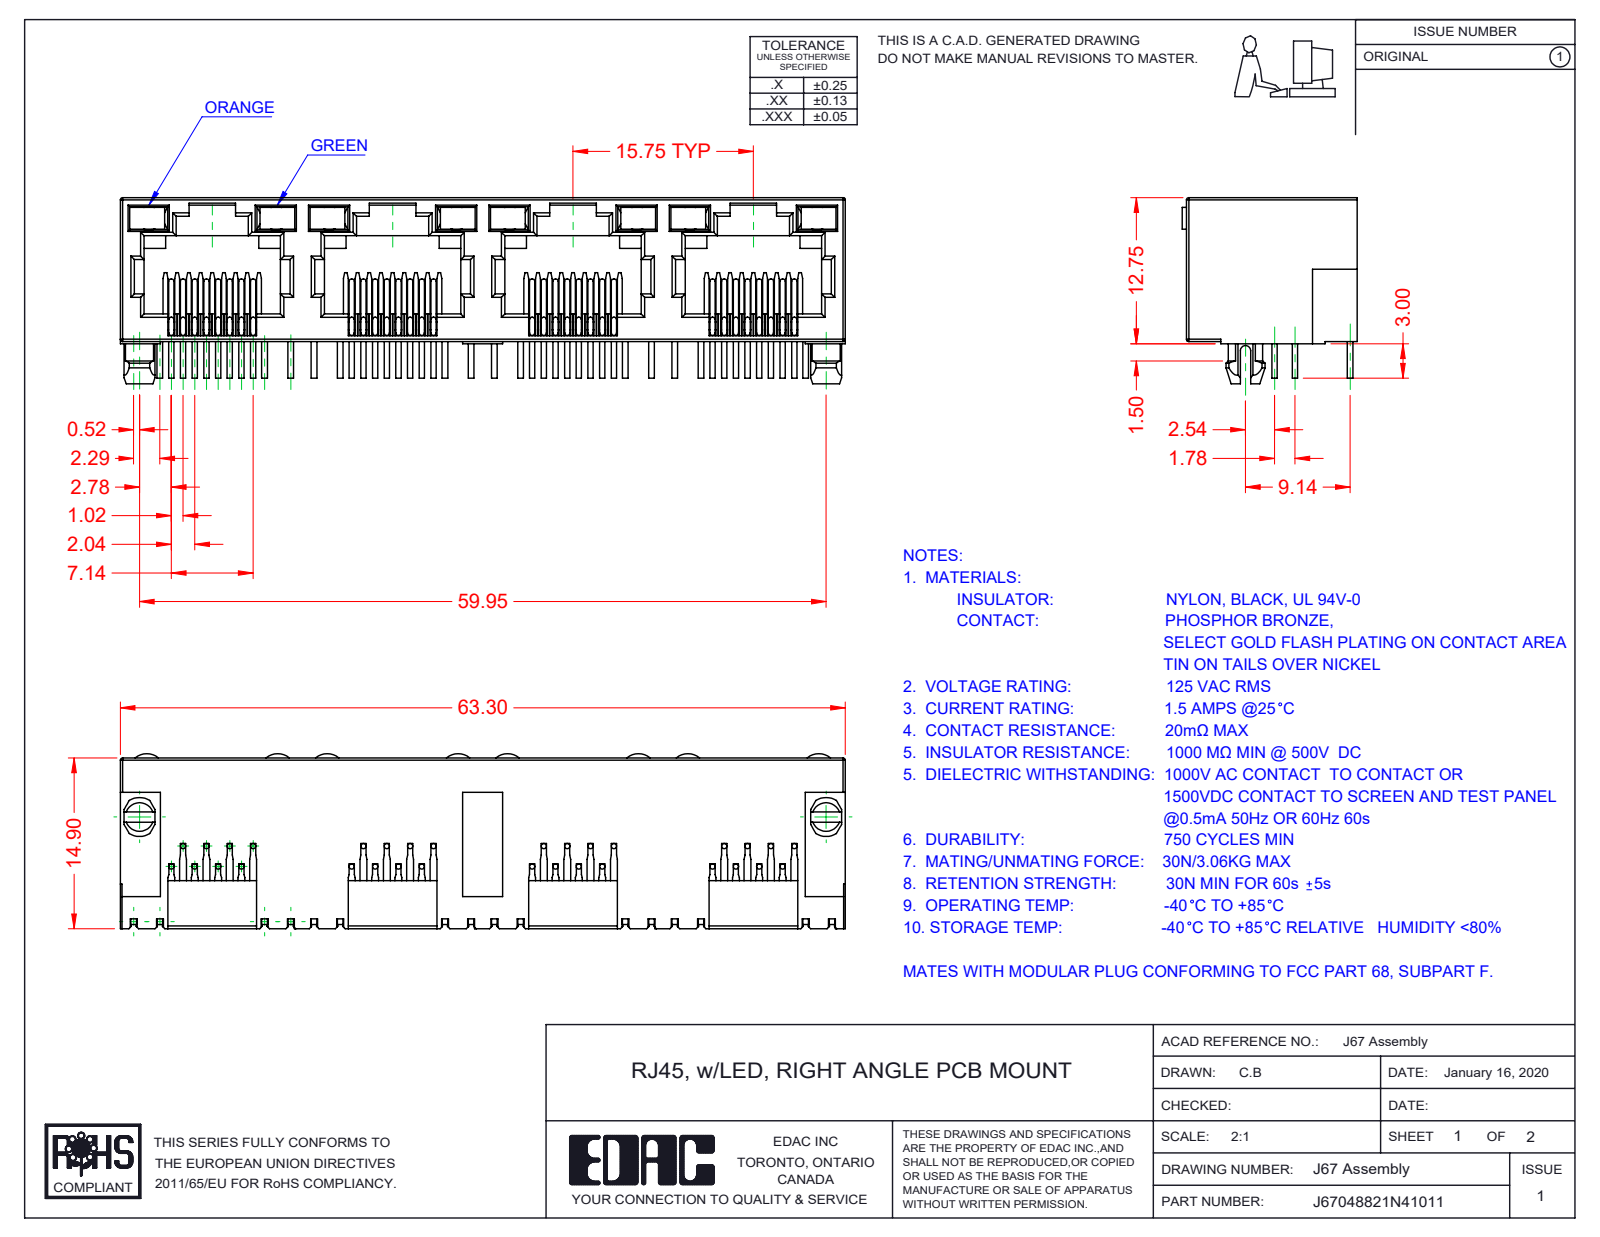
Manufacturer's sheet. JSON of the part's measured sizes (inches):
{"part_name": "67 Insulator; J67048822N43011; 67 LED RH_3-Green; 67 LED LH_4-Orange (+1 more)", "step_written_by": "SolidWorks 2016 (CONFIG_CONTROL_DESIGN)", "units": "inches", "bodies": {"solids": 41, "faces": 2465, "planar": 1781, "cylindrical": 476, "other": 208}, "overall_size": [2.492, 0.64, 0.602], "volume_in3": 0.315, "surface_area_in2": 17.94, "round_bosses_or_shafts": [[0.018, 96]], "partial_cylinders_radius": [[0.008, 66], [0.012, 29], [0.018, 9], [0.061, 8], [0.059, 2], [0.067, 2], [0.014, 1], [0.039, 1]], "face_to_face_distances": [0.02, 0.494, 0.074, 0.035, 0.394, 0.62, 0.039, 0.055, 0.433, 0.468]}
